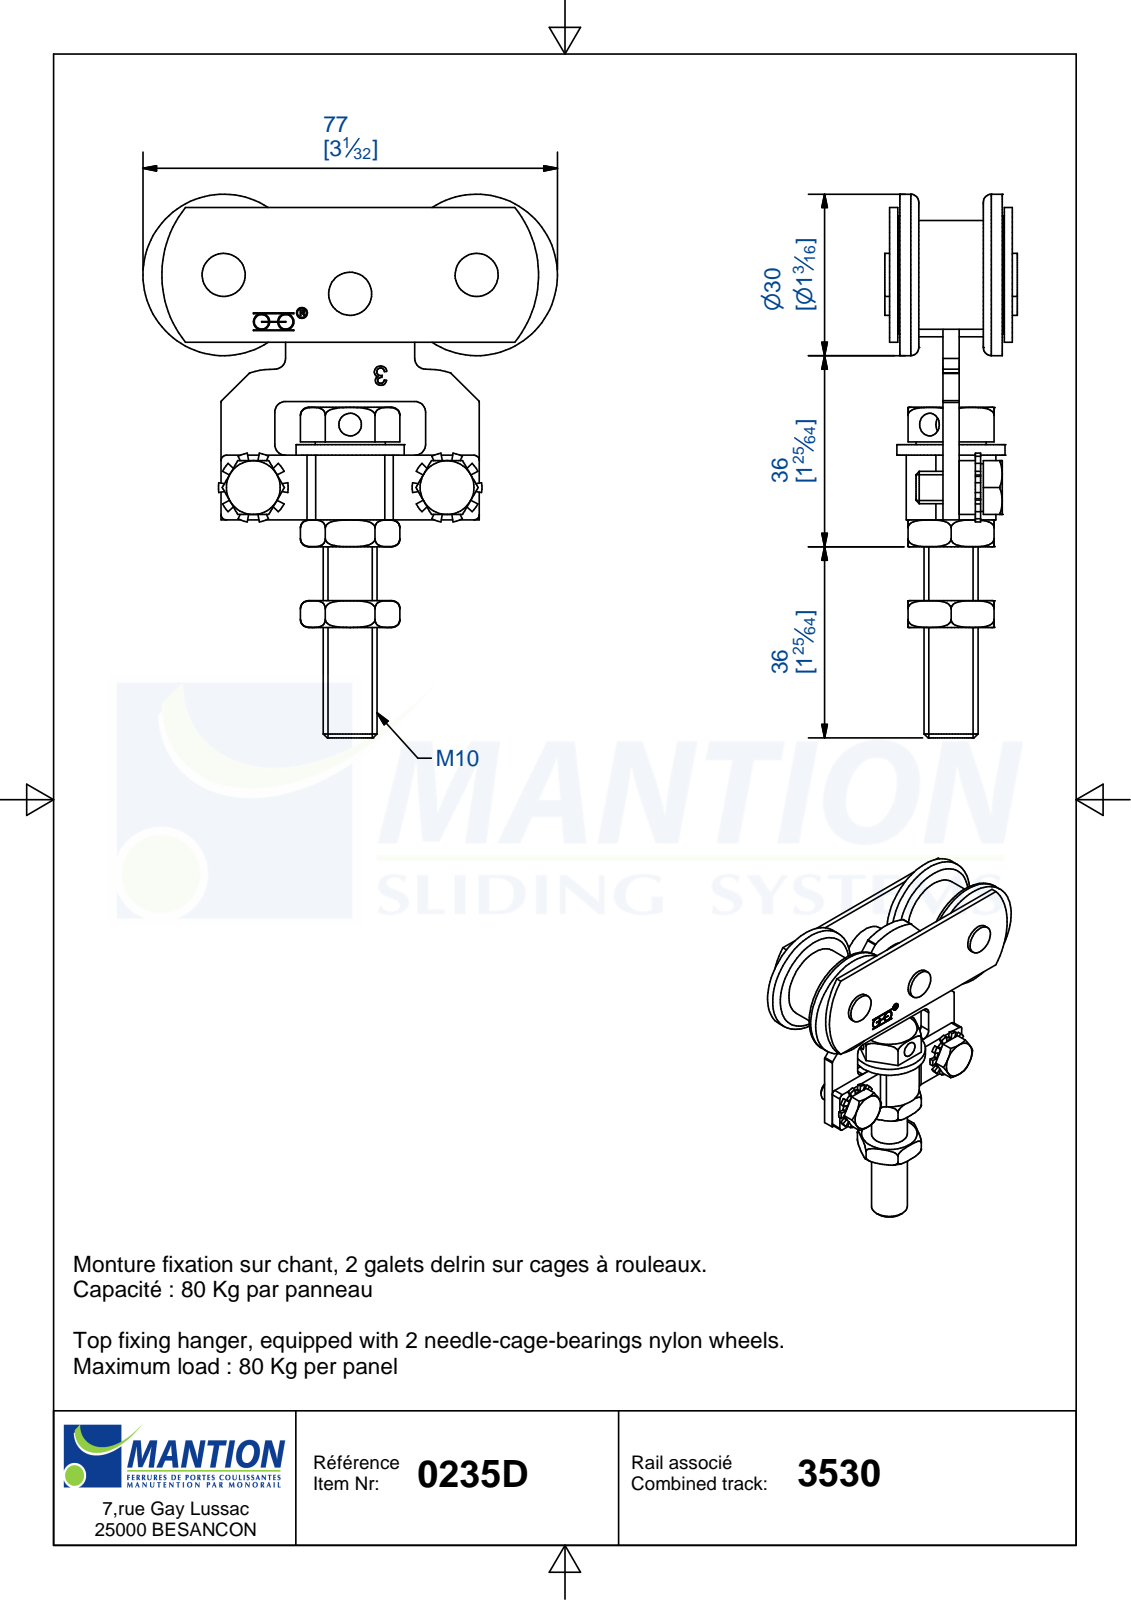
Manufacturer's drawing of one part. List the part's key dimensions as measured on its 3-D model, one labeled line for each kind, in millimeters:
Part name (STEP PRODUCT): 0235D; 13504; 15047; 15046 (+8 more)
STEP written by: Autodesk Inventor 2019 (AUTOMOTIVE_DESIGN)
Units: millimetres
Bodies: 30 solids, 622 faces (303 planar, 270 cylindrical, 49 other)
Overall size (bounding box): 101.5 × 77 × 24.6
Volume: 38 233 mm³ · Surface area: 35 787 mm²
Round holes (diameter × count): ⌀5.7 ×3, ⌀10.2 ×3, ⌀3 ×2, ⌀5 ×2, ⌀6.2 ×2, ⌀16.1 ×2, ⌀2 ×1, ⌀8.38 ×1, ⌀10.4 ×1
Round bosses / shafts (diameter × count): ⌀3 ×9, ⌀10 ×4, ⌀12.2 ×3, ⌀8 ×3, ⌀5.5 ×3, ⌀30 ×2, ⌀22 ×2, ⌀20.2 ×2
Partial cylindrical surfaces — rounded edges, fillets, slot ends (radius × count): R0.19 ×40, R1.55 ×22, R2 ×12, R1 ×4, R4.79 ×2, R5 ×2, R6.47 ×2, R7.7 ×2
Main face-to-face distances: 1.5, 21.3, 8.4, 11.4, 12.9, 9.9, 19.4, 3, 19.8, 11
Hole centre spacings: 23.76, 39.88, 40.25, 57.29, 3.42, 4.5, 7.68, 9.64
